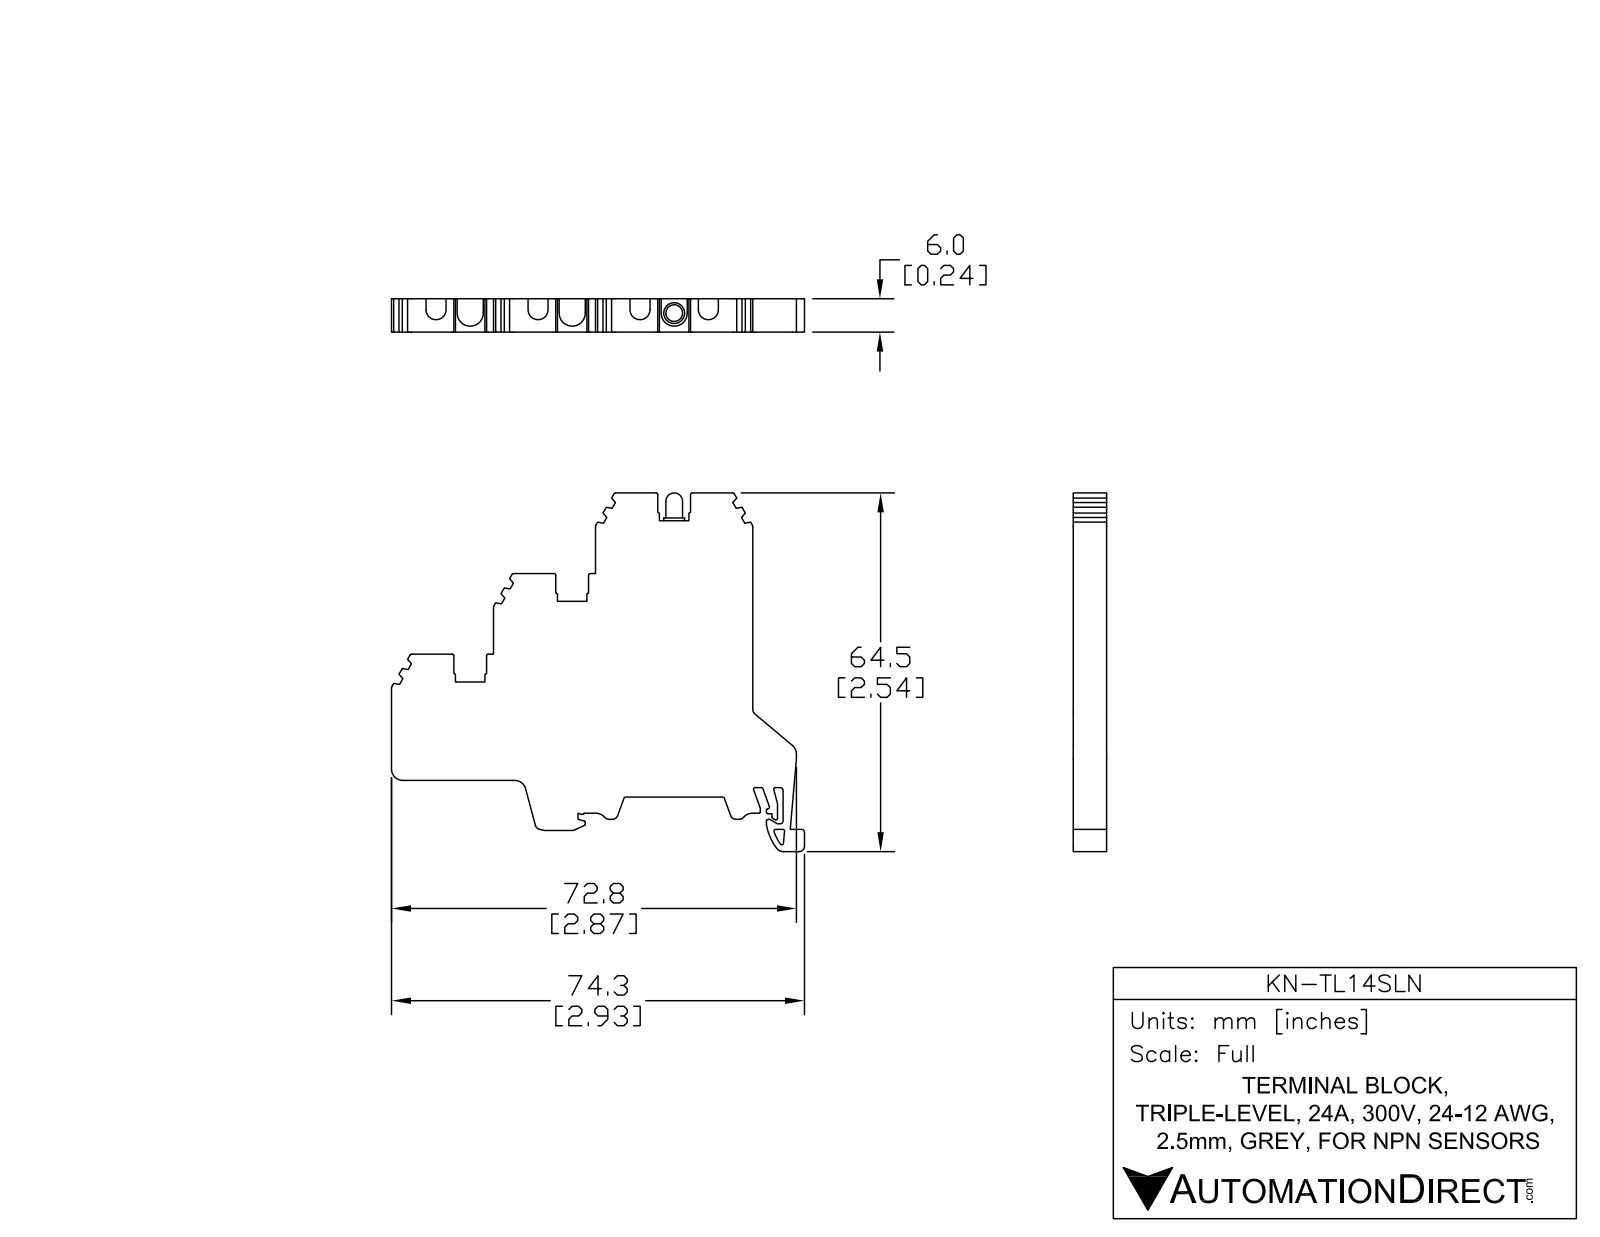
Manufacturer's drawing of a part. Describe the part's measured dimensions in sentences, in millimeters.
The part is named "KN-TL14SLN". Its 3-D file was written by "SolidWorks 2014 (AUTOMOTIVE_DESIGN)". It is 3 solids with 228 faces: 151 planar, 76 cylindrical and 1 other. Overall it measures 74.3 by 64.51 by 6 millimeters. Its volume is 16 307 cubic millimeters and its surface area 7 900 square millimeters. Round bosses or shafts: 1 of diameter 3.75, 1 of diameter 3, 1 of diameter 2.5. Partial cylindrical surfaces (rounded edges, fillets, slot ends): 23 of radius 0.3, 8 of radius 1, 7 of radius 0.5, 6 of radius 0.2, 4 of radius 1.8, 4 of radius 2, 3 of radius 2.35, 2 of radius 2.13. The main face-to-face distances are 6, 14.5, 18.35, 1, 3, 4, 5, 54.7, 29, 9.5.
